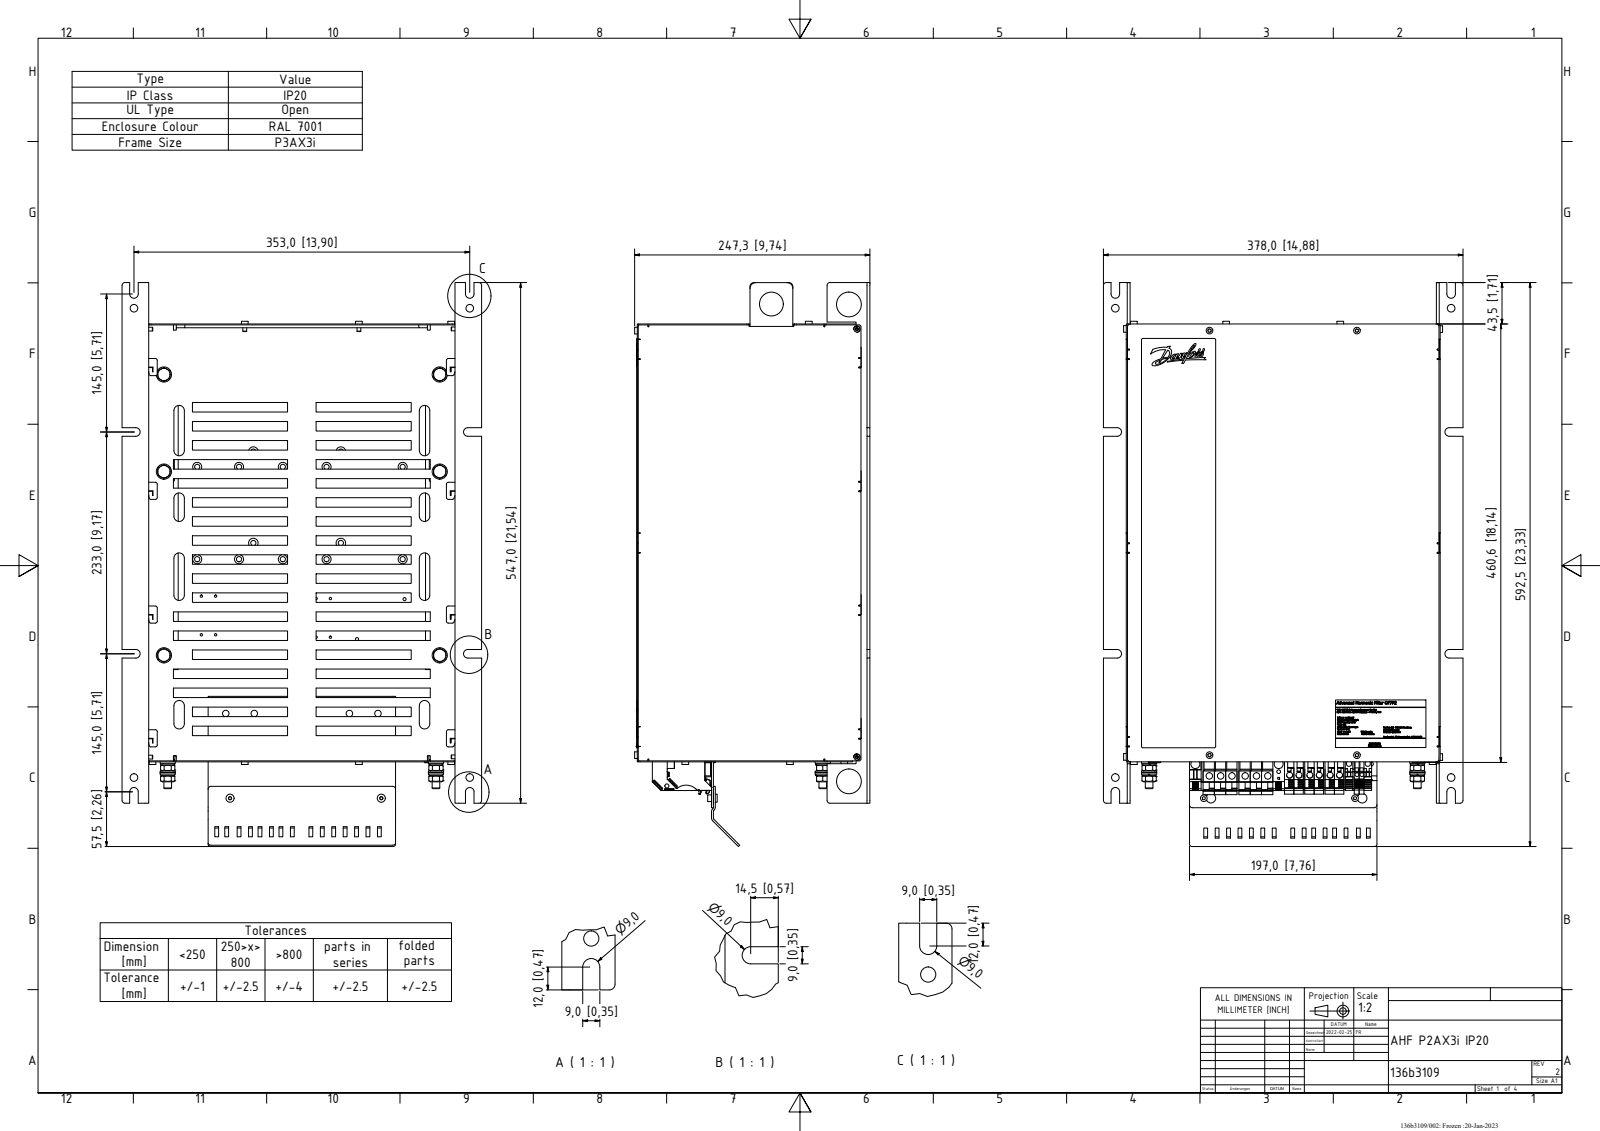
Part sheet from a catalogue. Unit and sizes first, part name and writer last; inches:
Units: inches
Overall size (bounding box): 23.374 × 17.022 × 15.418
Round holes (diameter × count): ⌀0.249 ×6, ⌀0.268 ×6, ⌀0.315 ×4, ⌀0.157 ×2, ⌀0.22 ×2, ⌀0.37 ×2, ⌀0.492 ×2, ⌀0.984 ×2, ⌀1.024 ×2, ⌀0.787 ×1, ⌀1.339 ×1, ⌀1.89 ×1
Round bosses / shafts (diameter × count): ⌀0.276 ×13, ⌀0.583 ×6, ⌀0.512 ×2, ⌀0.445 ×2, ⌀0.315 ×2, ⌀0.26 ×2, ⌀4.213 ×1, ⌀3.652 ×1
Partial cylindrical surfaces — rounded edges, fillets, slot ends (radius × count): R0.177 ×8, R0.051 ×1, R0.114 ×1, R0.144 ×1, R0.154 ×1, R0.168 ×1, R0.266 ×1, R0.593 ×1
Main face-to-face distances: 0.059, 8.835, 8.776, 0.116, 8.952, 8.893, 12.988, 0.117, 12.871, 0.119
Hole centre spacings: 0.839, 0.39, 0.449, 0.469, 1.484, 1.953, 3.209, 13.897
Volume: 137.9 in³ · Surface area: 2 317 in²
Bodies: 13 solids, 1686 faces (1428 planar, 203 cylindrical, 55 other)
STEP written by: CREO PARAMETRIC BY PTC INC, 2020342 (CONFIG_CONTROL_DESIGN)
